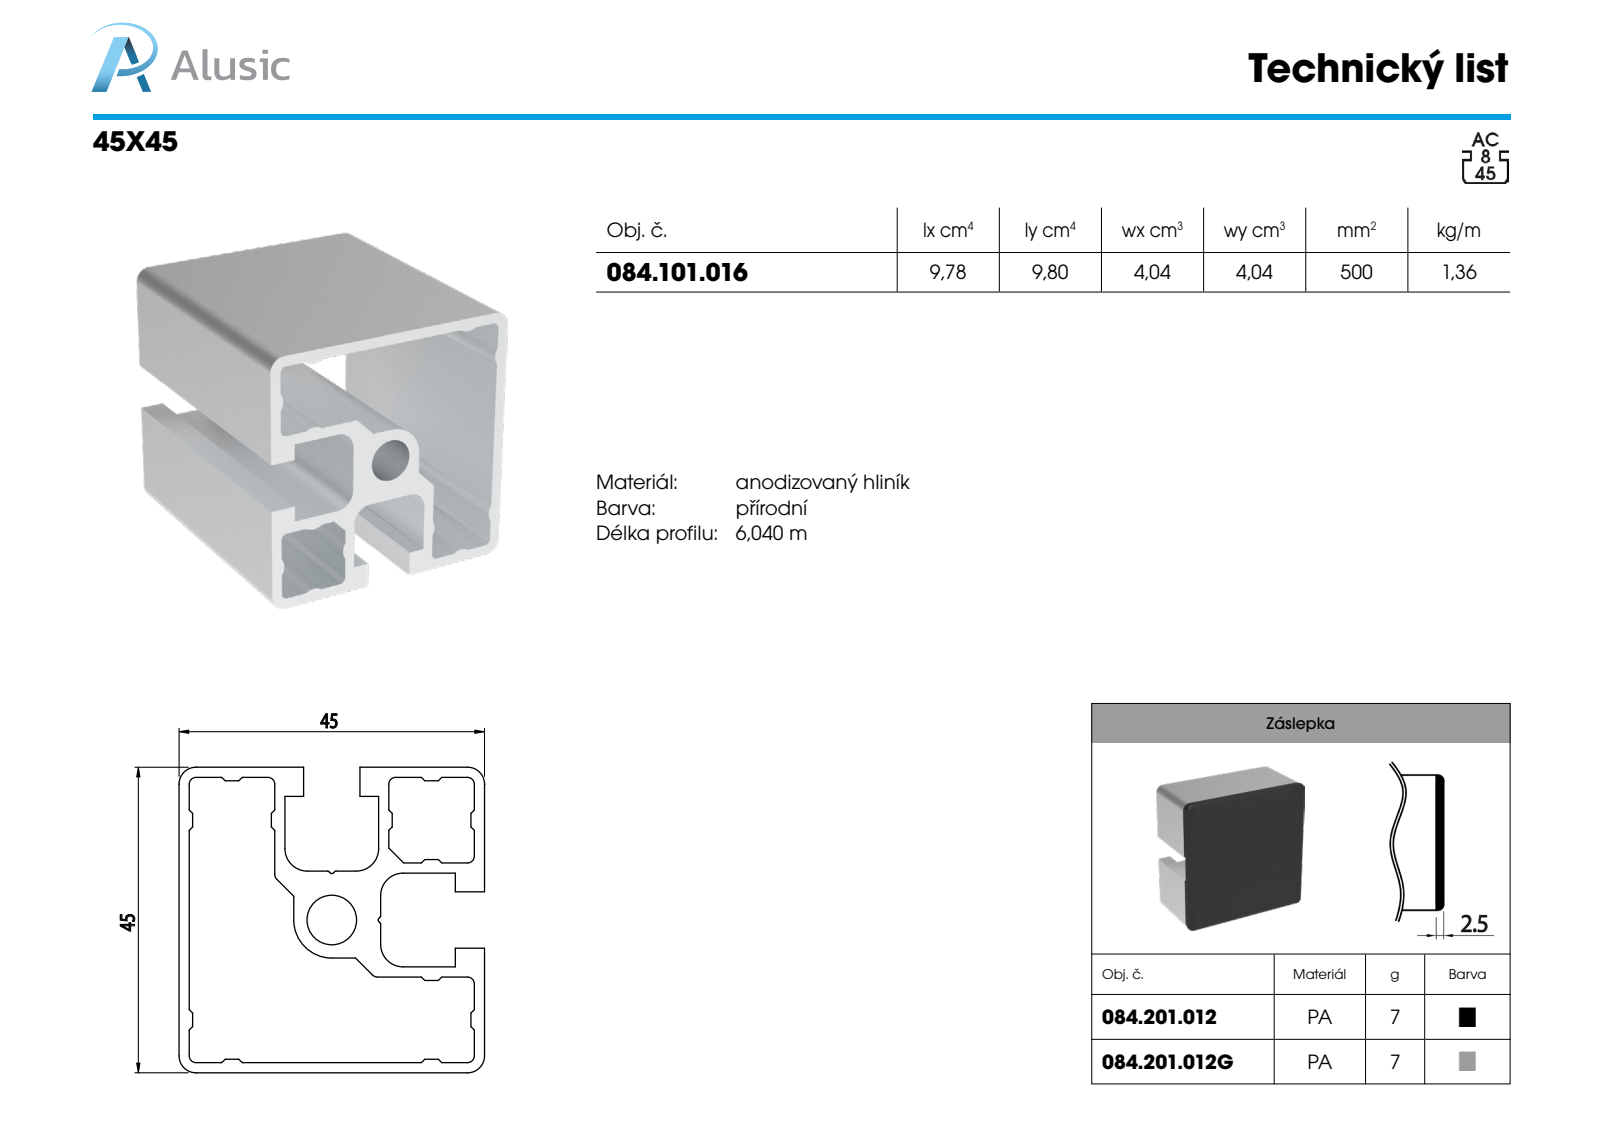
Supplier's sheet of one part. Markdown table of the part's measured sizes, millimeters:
| quantity | value |
| --- | --- |
| part name | 084.101.016 |
| STEP written by | SolidWorks 2018 (AUTOMOTIVE_DESIGN) |
| units | millimeters |
| bodies | 1 solid, 83 faces (49 planar, 34 cylindrical, 0 other) |
| overall size | 100 × 45 × 45 |
| volume | 54 826 mm³ |
| surface area | 49 277 mm² |
| round holes (diameter × count) | 7.3 × 1 |
| partial cylindrical surfaces (radius × count) | 2.72 × 12, 1 × 8, 2.5 × 4, 3 × 4, 5.6 × 1 |
| main face-to-face distances | 1.8, 43.2, 13.8, 45, 29.4, 15.6, 27.6, 41.4, 12, 31.2 |
